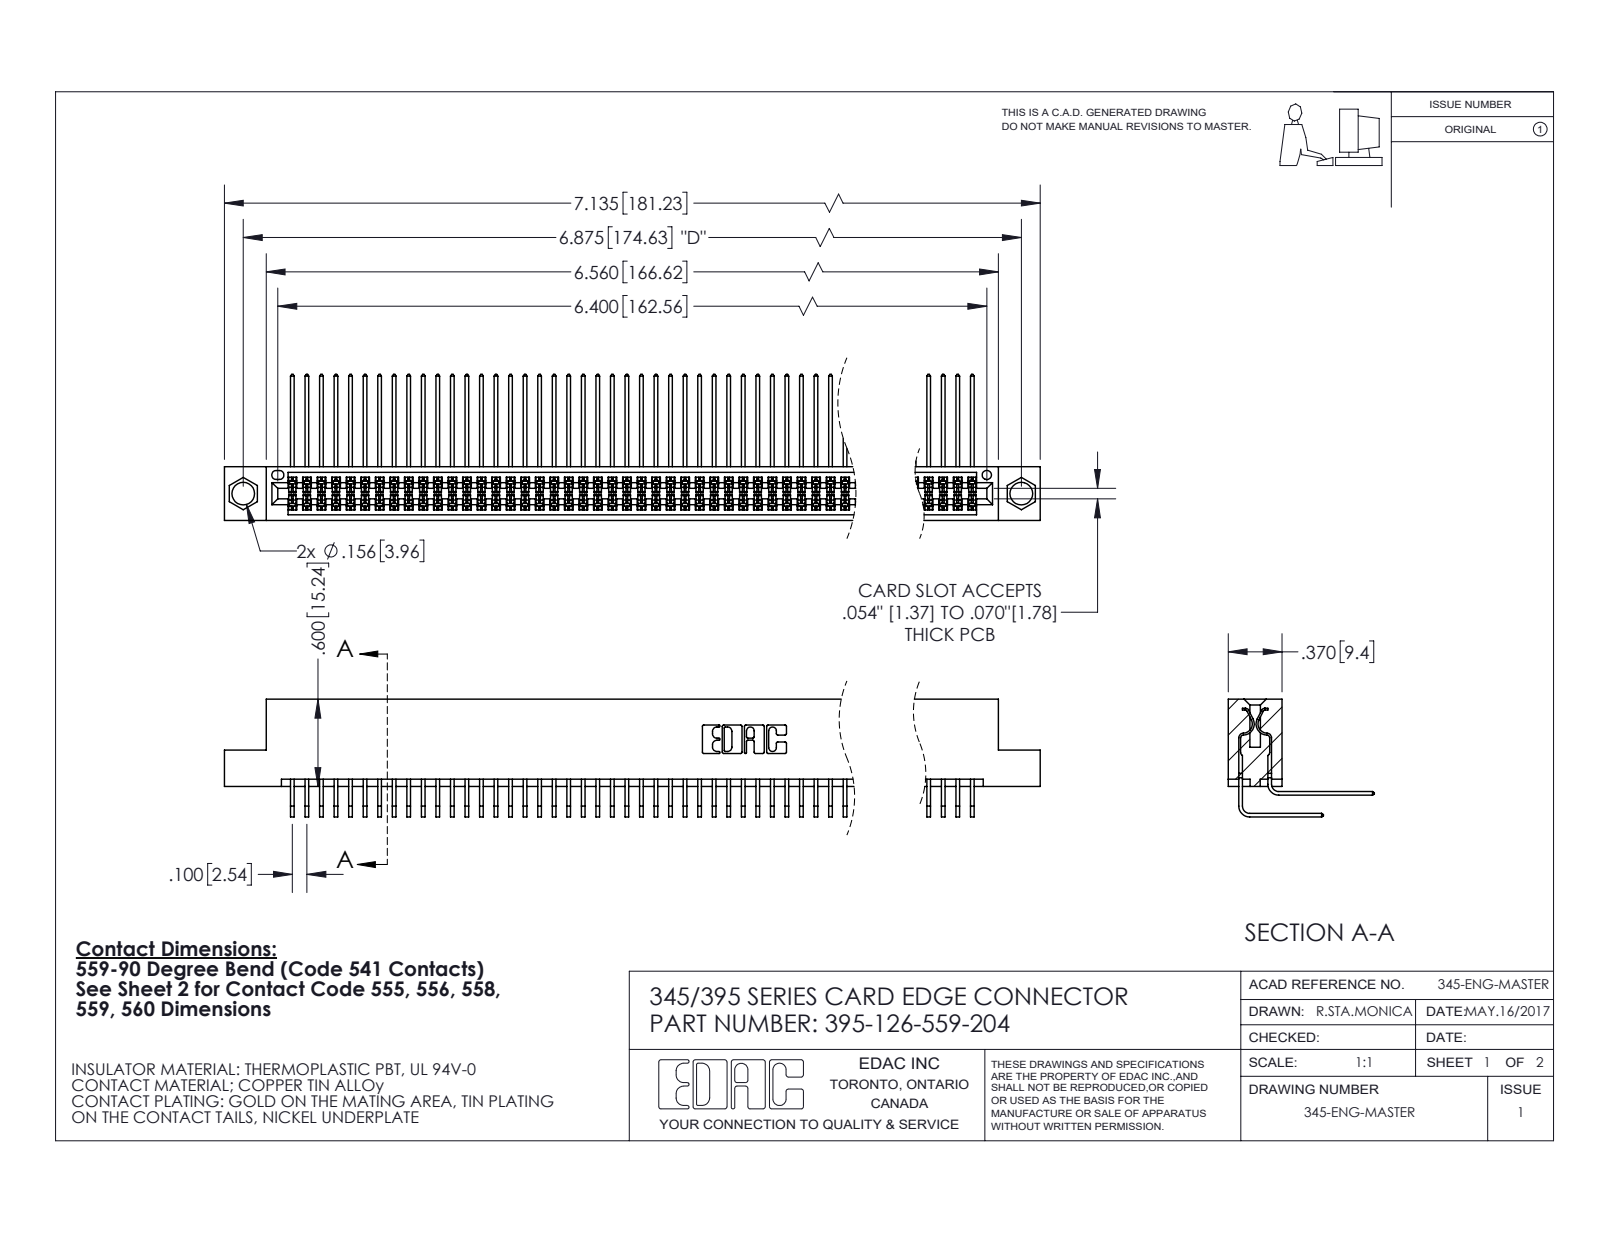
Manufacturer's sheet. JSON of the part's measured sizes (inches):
{"part_name": "395-126-559-204; 345-292-001_558 559 Tail - 1; 345-292-001_559 Tail - 2; 345 Part_Flush Mounting Lugs - 0.156 Dia-TI", "step_written_by": "SolidWorks 2020 (CONFIG_CONTROL_DESIGN)", "units": "inches", "bodies": {"solids": 127, "faces": 6692, "planar": 4504, "cylindrical": 2188, "other": 0}, "overall_size": [7.135, 1.005, 0.809], "volume_in3": 1.124, "surface_area_in2": 47.9, "round_holes": [[0.156, 2], [0.064, 1]], "partial_cylinders_radius": [[0.006, 190], [0.01, 22], [0.007, 6], [0.031, 6], [0.026, 3], [0.014, 2], [0.019, 2], [0.022, 2]], "face_to_face_distances": [0.072, 0.298, 0.2, 0.37, 0.098, 0.272, 0.025, 0.225, 0.175, 0.15], "hole_center_spacings": [0.27, 6.639, 6.875]}
